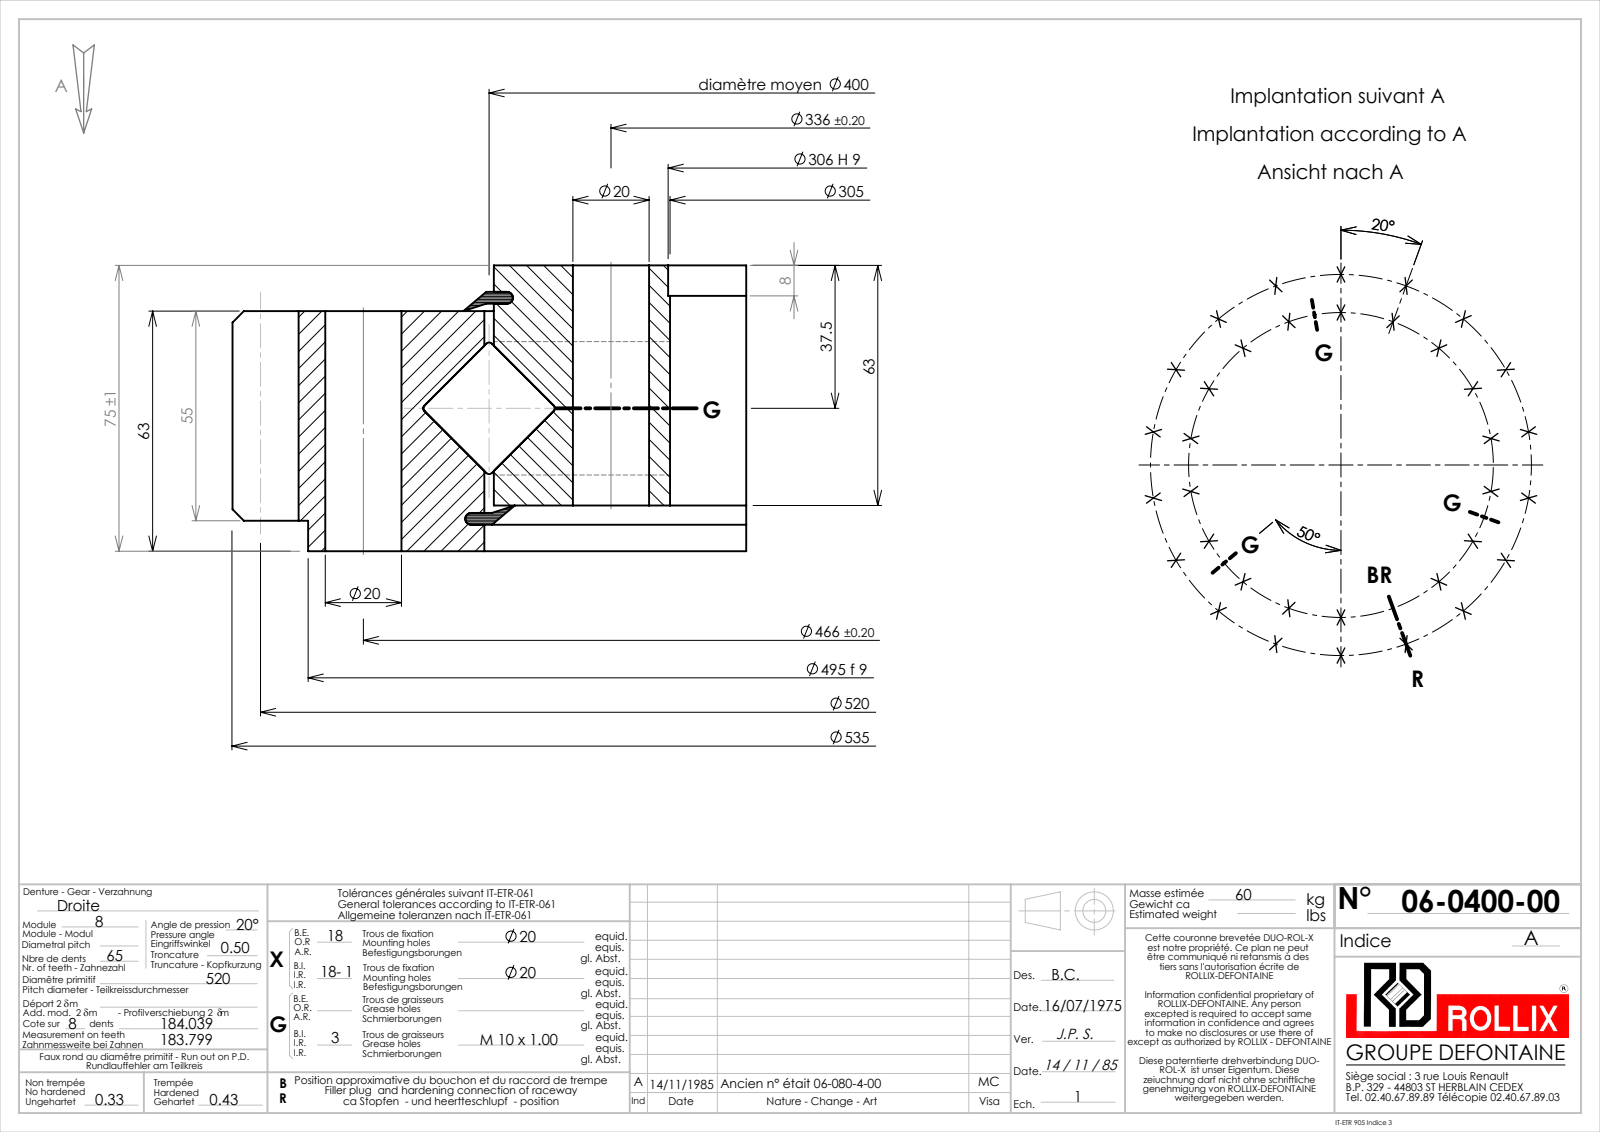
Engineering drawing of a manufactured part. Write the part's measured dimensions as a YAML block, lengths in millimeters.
part_name: "06-0400-00"
step_written_by: "SolidWorks 2016 (CONFIG_CONTROL_DESIGN)"
units: millimeters
bodies: {solids: 5, faces: 546, planar: 146, cylindrical: 227, other: 173}
overall_size: [534.98, 534.85, 75]
volume: 7039000
surface_area: 930179
round_holes:
  - {diameter: 20, count: 35}
  - {diameter: 9, count: 3}
  - {diameter: 305, count: 1}
  - {diameter: 306, count: 1}
  - {diameter: 402.5, count: 1}
round_bosses_or_shafts:
  - {diameter: 495, count: 1}
  - {diameter: 397.5, count: 1}
  - {diameter: 25, count: 1}
partial_cylinders:
  - {radius: 250, count: 1}
  - {radius: 267.5, count: 1}
face_to_face_distances: [63, 12, 51, 75, 10.05, 64.95, 1.95, 52.95, 6.95, 68.05]
hole_center_spacings: [233, 395.07, 168, 208.25, 80.92, 159.38, 299.54, 458.92]
